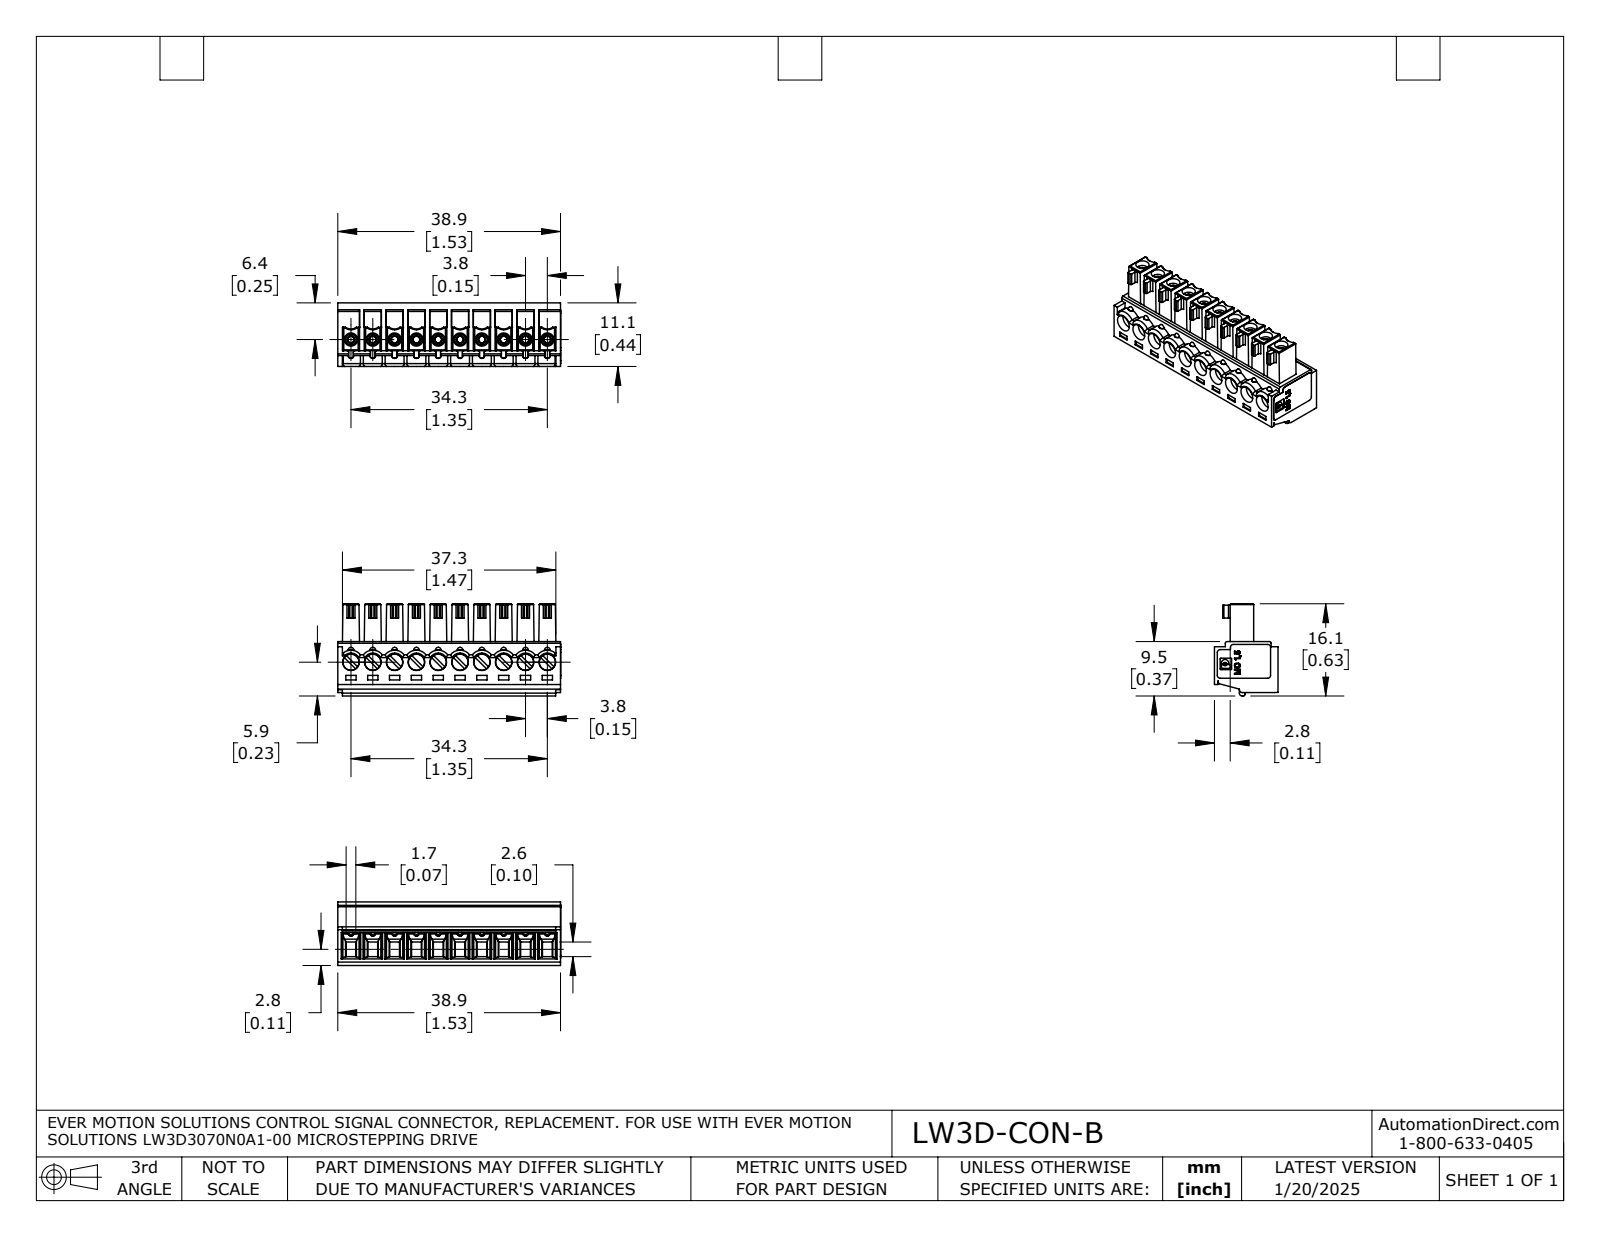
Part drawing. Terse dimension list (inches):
name: LW3D-CON-B
written by: SolidWorks 2021 (AUTOMOTIVE_DESIGN)
unit: in
bodies: 31 solids, 1476 faces (923 planar, 453 cylindrical, 100 other)
size: 1.532 × 0.634 × 0.437
volume: 0.203 in³; area: 10.65 in²
holes: 10× ⌀0.046, 10× ⌀0.047, 10× ⌀0.079, 10× ⌀0.114
bosses: 10× ⌀0.11, 1× ⌀0.012
rounds: 42× R0.006, 30× R0.02, 23× R0.012, 21× R0.008, 21× R0.039, 20× R0.03, 10× R0.065, 10× R0.083
face distances: 0.15, 0.3, 0.45, 0.6, 0.75, 0.9, 0.102, 0.048, 1.05, 0.252
hole spacings: 0.15, 0.3, 0.45, 0.6, 0.75, 0.9, 1.05, 1.2
